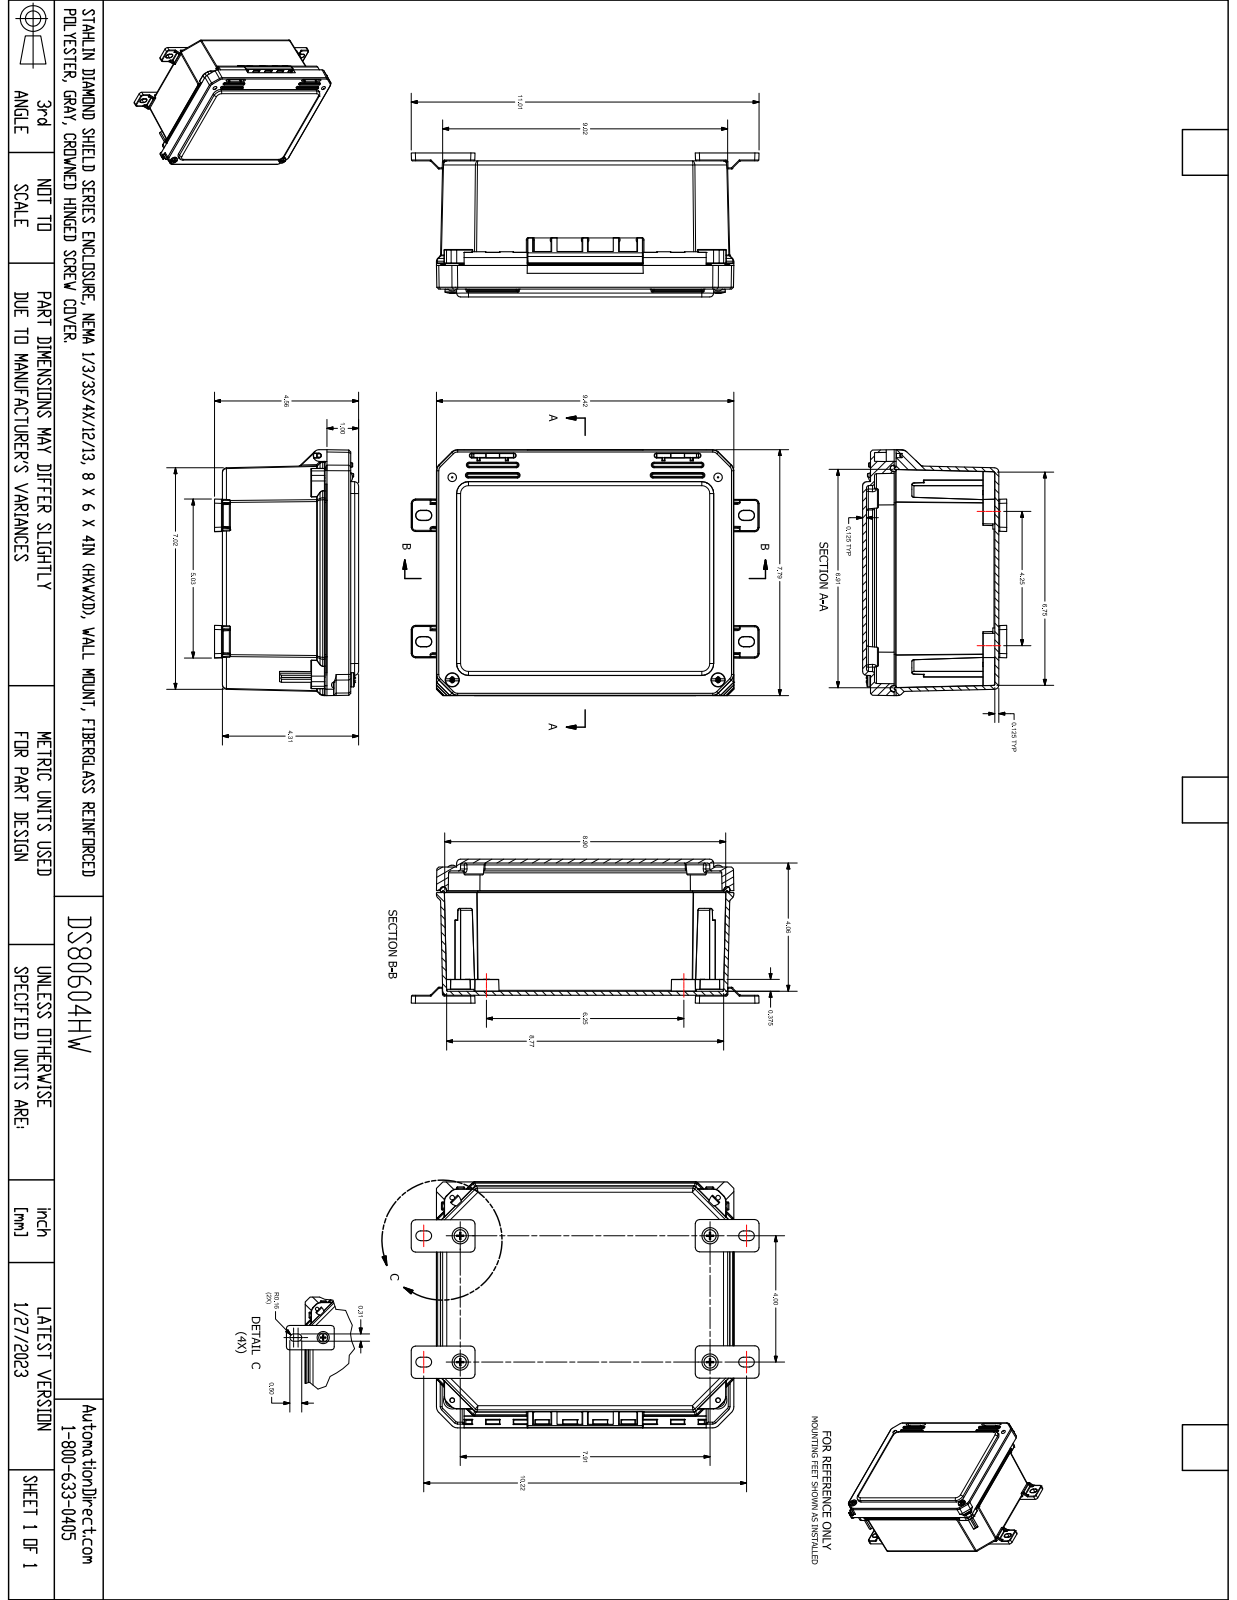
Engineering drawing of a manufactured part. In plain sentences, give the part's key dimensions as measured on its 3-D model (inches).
The part is named "FR80604HW". Its 3-D file was written by "SolidWorks 2021 (AUTOMOTIVE_DESIGN)". It is 23 solids with 2099 faces: 639 planar, 824 cylindrical and 636 other. Overall it measures 9.417 by 7.806 by 4.529 inches. Its volume is 44.3 cubic inches and its surface area 602.4 square inches. Round holes: 8 of diameter 0.152, 8 of diameter 0.159, 4 of diameter 0.156, 4 of diameter 0.252, 4 of diameter 0.253, 3 of diameter 0.137, 2 of diameter 0.15, 2 of diameter 0.219, 2 of diameter 0.227, 2 of diameter 0.313. Round bosses or shafts: 8 of diameter 0.27, 4 of diameter 0.87, 4 of diameter 0.262, 2 of diameter 0.45, 2 of diameter 0.435, 2 of diameter 0.209, 2 of diameter 0.199, 2 of diameter 0.135. Partial cylindrical surfaces (rounded edges, fillets, slot ends): 120 of radius 0.01, 94 of radius 0.005, 77 of radius 0.02, 51 of radius 0.03, 24 of radius 0.03, 24 of radius 0.09, 24 of radius 0.096, 23 of radius 0.063. The main face-to-face distances are 0.125, 0.125, 4.059, 4.184, 4.309, 4.184, 0.25, 3.934, 0.124, 0.375. The hole center spacings are 7.411, 8.415, 8.414, 9.065, 4.207, 4.25, 6.25, 1.529.
